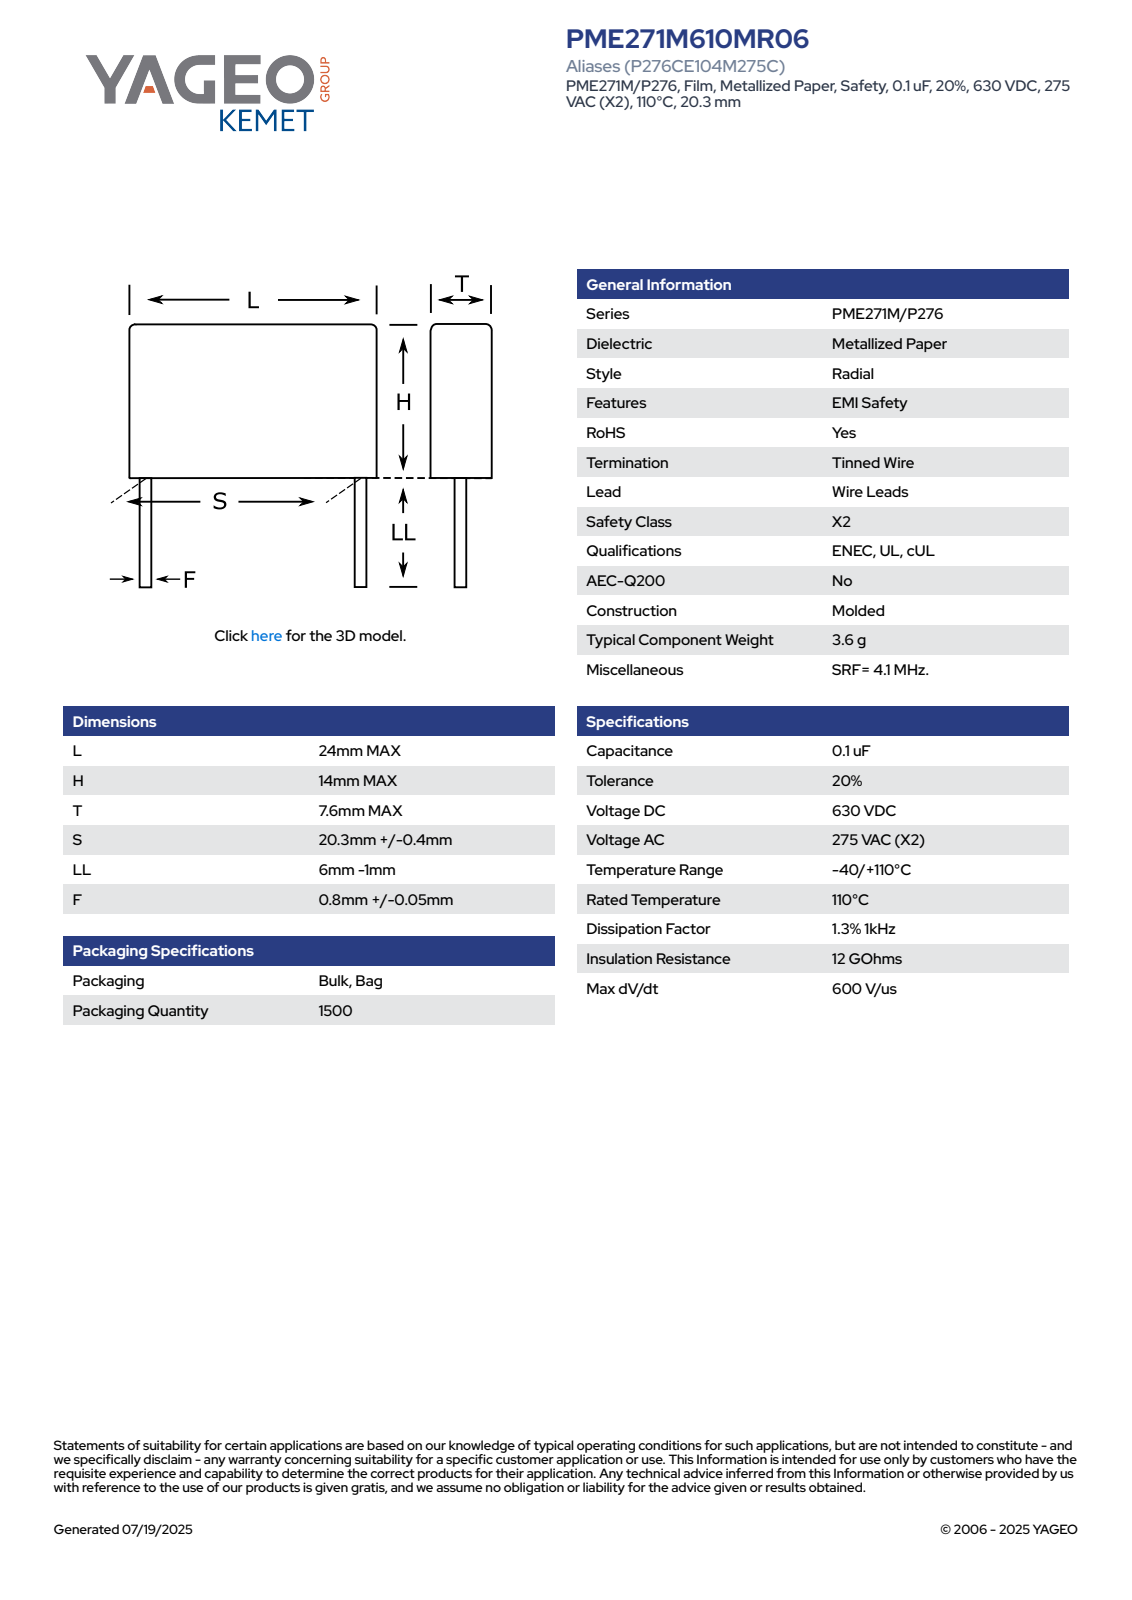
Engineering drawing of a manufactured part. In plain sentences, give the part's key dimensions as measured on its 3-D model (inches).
The part is named "CFR_MOLDED_24X14X7.6_L24H14T7.6S20.3LL5F0.85". Its 3-D file was written by "SolidWorks 2014 (AUTOMOTIVE_DESIGN)". It is 4 solids with 73 faces: 65 planar, 8 cylindrical and 0 other. Overall it measures 0.945 by 0.748 by 0.3 inches. Its volume is 0.156 cubic inches and its surface area 2 square inches. Round bosses or shafts: 2 of diameter 0.033. Partial cylindrical surfaces (rounded edges, fillets, slot ends): 4 of radius 0.02. The main face-to-face distances are 0.299, 0.551, 0.945, 0.197, 0.748, 0.231, 0.513, 0.316, 0.235, 0.428.
